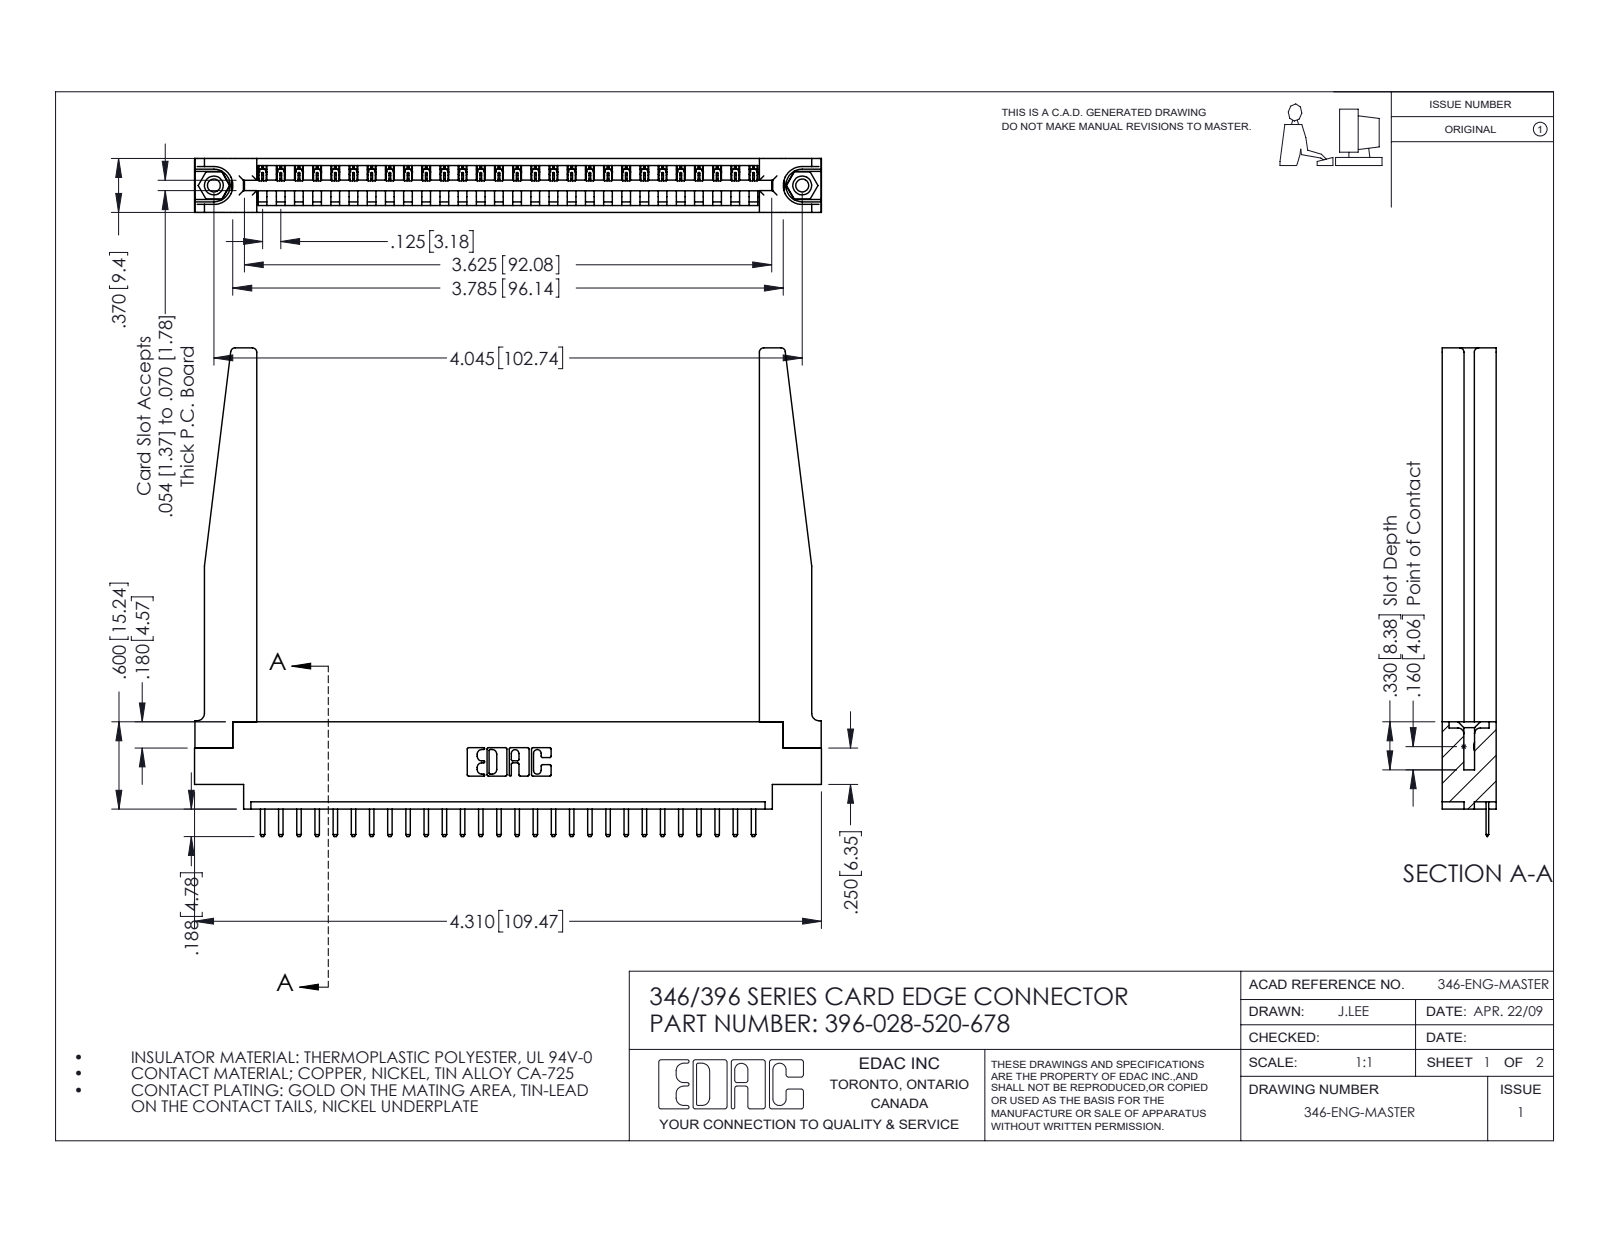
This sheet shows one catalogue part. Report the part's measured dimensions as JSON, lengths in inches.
{"part_name": "346 Part_0.170 Offset - 0.156 Dia-TH; 396-028-520-678; 345-250-001_345-250-001-102; 345-292-001_345-293-120 (+1 more)", "step_written_by": "SolidWorks 2016 (CONFIG_CONTROL_DESIGN)", "units": "inches", "bodies": {"solids": 33, "faces": 2096, "planar": 1398, "cylindrical": 646, "other": 52}, "overall_size": [4.31, 3.358, 0.37], "volume_in3": 1.041, "surface_area_in2": 29.39, "round_holes": [[0.089, 2], [0.125, 2], [0.156, 2], [0.064, 1]], "round_bosses_or_shafts": [[0.155, 2]], "partial_cylinders_radius": [[0.01, 58], [0.006, 56], [0.01, 22], [0.03, 8], [0.007, 6], [0.031, 6], [0.026, 3], [0.031, 2]], "face_to_face_distances": [0.37, 0.048, 0.322, 0.148, 0.072, 0.15, 0.25, 0.222, 0.1, 0.174], "hole_center_spacings": [0.246, 3.837, 4.045]}
